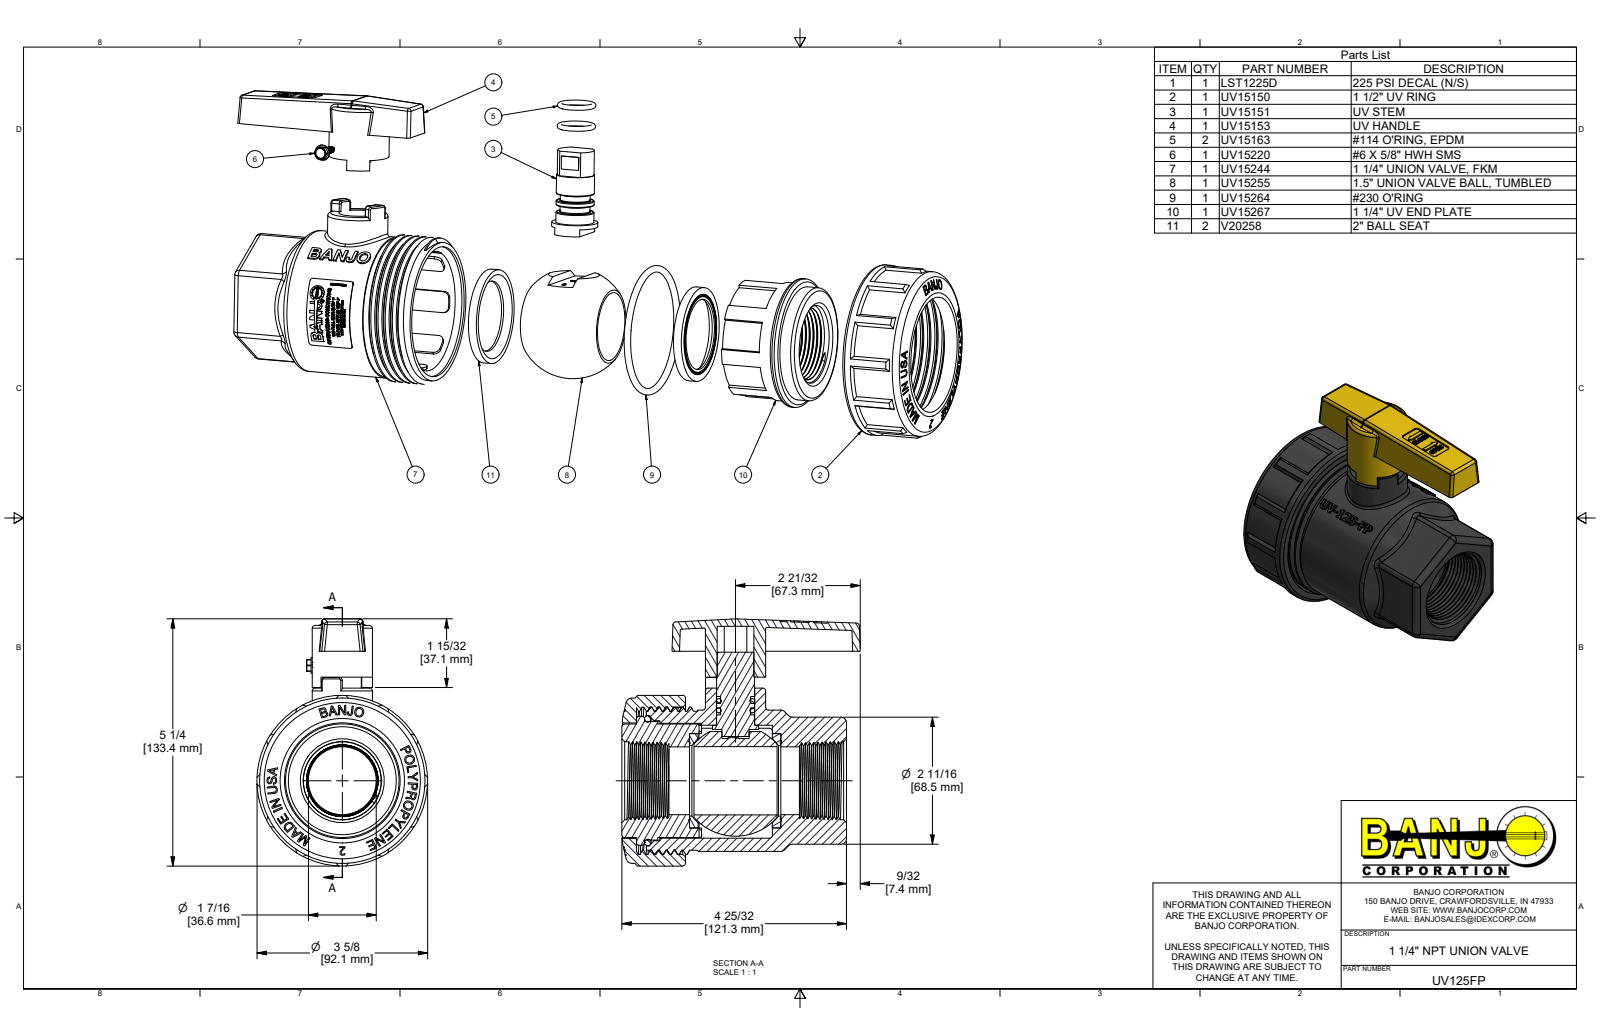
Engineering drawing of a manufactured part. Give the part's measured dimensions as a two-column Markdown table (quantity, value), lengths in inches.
| quantity | value |
| --- | --- |
| part name | UV125FP; UV15244; UVL1000-D3.000; UV15150 (+8 more) |
| STEP written by | Autodesk Inventor 2019 (AUTOMOTIVE_DESIGN) |
| units | inches |
| bodies | 13 solids, 2852 faces (1403 planar, 381 cylindrical, 1068 other) |
| overall size | 48.762 × 5.25 × 3.625 |
| volume | 29.67 in³ |
| surface area | 500.7 in² |
| round holes (diameter × count) | 0.813 × 1, 1.44 × 1, 1.45 × 1, 1.5 × 1, 2.007 × 1, 2.01 × 1, 2.44 × 1, 2.455 × 1, 2.55 × 1, 2.77 × 1, 2.945 × 1 |
| round bosses / shafts (diameter × count) | 3.625 × 1, 3.51 × 1, 3.126 × 1, 3.125 × 1, 3 × 1, 2.95 × 1, 2.74 × 1, 2.52 × 1 |
| partial cylindrical surfaces (radius × count) | 0.06 × 26, 0.125 × 24, 0.03 × 18, 0.25 × 3, 0.479 × 2, 0.826 × 2, 0.139 × 1, 0.39 × 1 |
| main face-to-face distances | 2.37, 1.127, 1.941, 3.068, 0.16, 1.33, 3.378, 1.437, 0.31, 1.738 |
